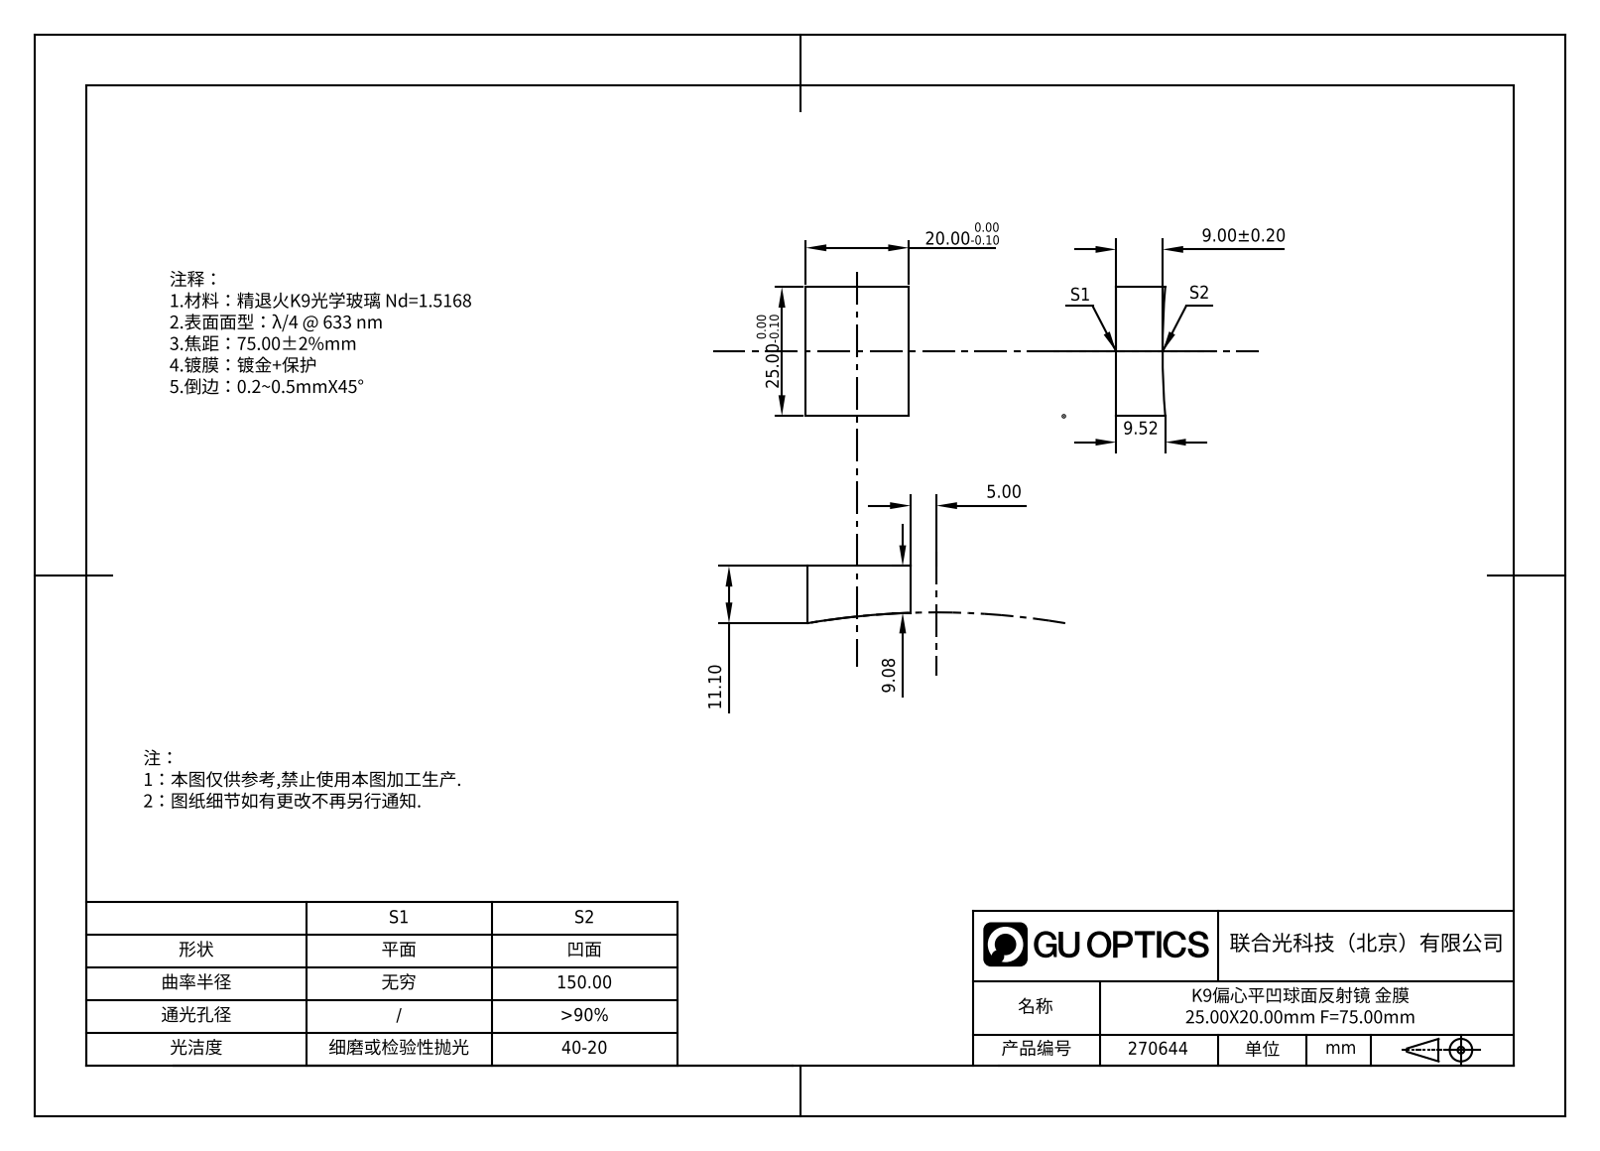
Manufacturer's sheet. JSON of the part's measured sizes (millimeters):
{"part_name": "270644", "step_written_by": "SolidWorks 2020 (CONFIG_CONTROL_DESIGN)", "units": "millimeters", "bodies": {"solids": 1, "faces": 7, "planar": 5, "cylindrical": 0, "other": 2}, "overall_size": [25, 20, 11.63], "volume_mm3": 5020, "surface_area_mm2": 1932, "face_to_face_distances": [20, 25]}
